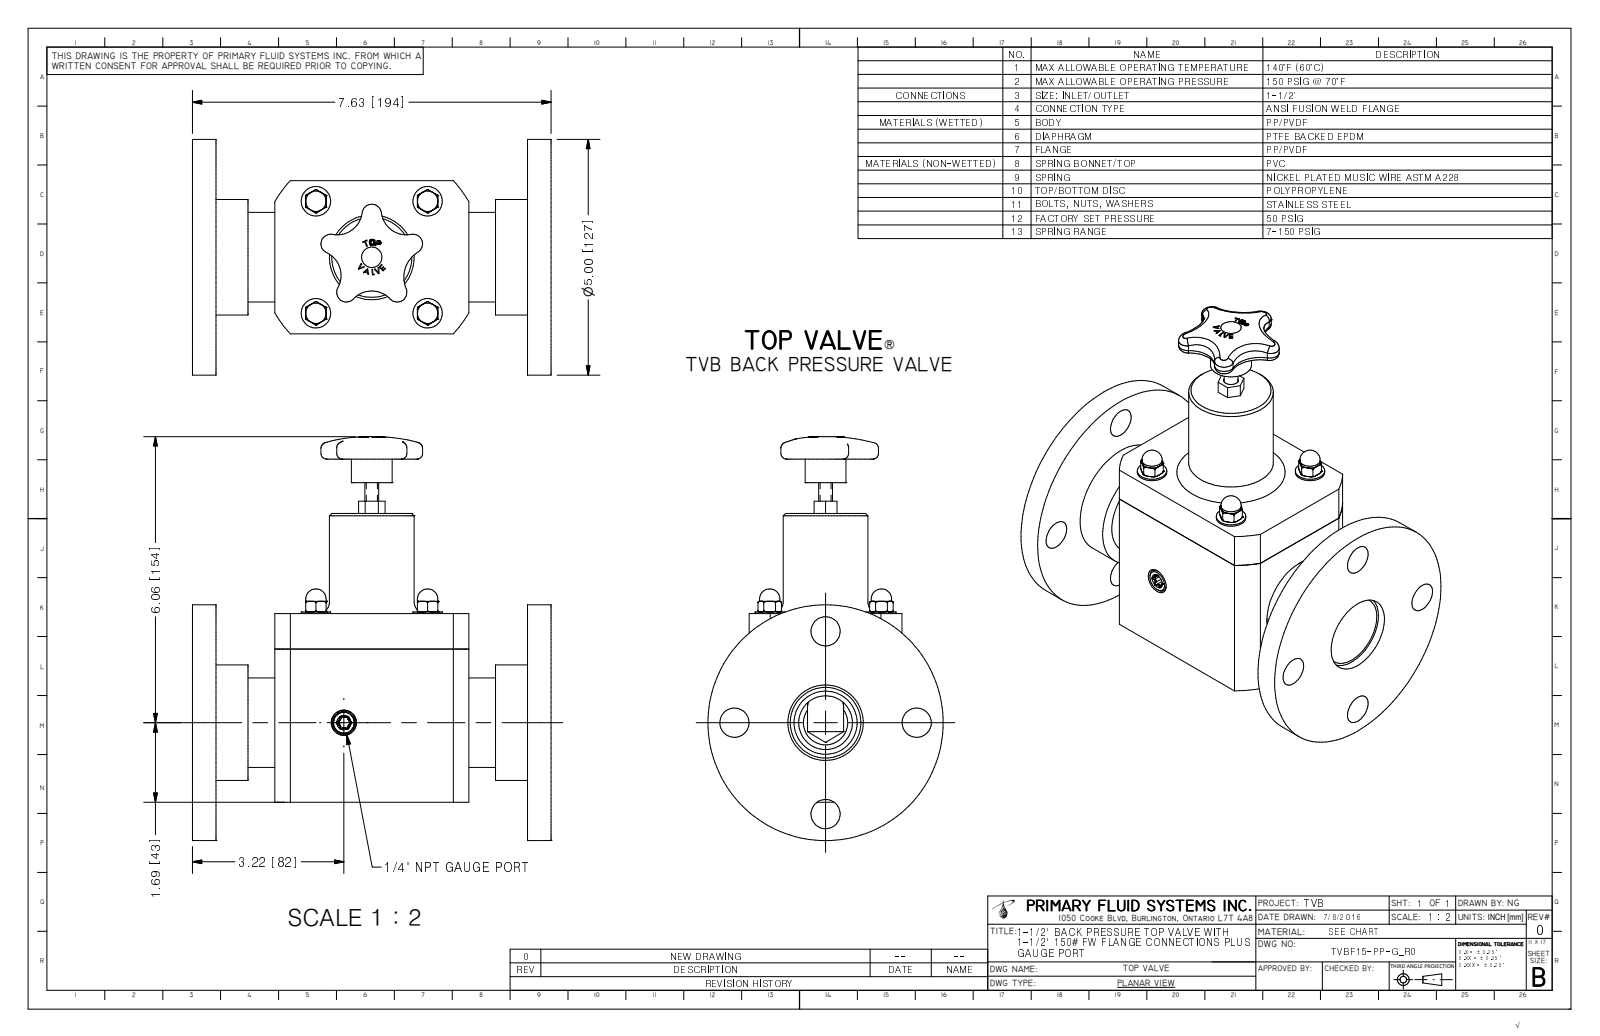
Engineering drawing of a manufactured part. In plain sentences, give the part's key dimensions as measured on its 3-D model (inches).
The part is named "TVBF15-PP-G_R0". Its 3-D file was written by "Autodesk Inventor 2009 (AUTOMOTIVE_DESIGN)". It is 1 solid with 383 faces: 160 planar, 67 cylindrical and 156 other. Overall it measures 8.565 by 7.625 by 5 inches. Its volume is 77.72 cubic inches and its surface area 239.2 square inches. Round holes: 4 of diameter 0.175, 4 of diameter 0.62, 1 of diameter 1.5, 1 of diameter 1.6. Round bosses or shafts: 4 of diameter 0.625, 4 of diameter 0.433, 4 of diameter 0.375, 1 of diameter 5, 1 of diameter 2.45, 1 of diameter 1.9, 1 of diameter 1.8, 1 of diameter 0.87. Partial cylindrical surfaces (rounded edges, fillets, slot ends): 6 of radius 0.027, 5 of radius 0.085, 5 of radius 0.205, 4 of radius 0.536, 4 of radius 0.656, 1 of radius 0.625, 1 of radius 0.745, 1 of radius 2.375. The main face-to-face distances are 0.5, 7.125, 7.625, 6.625, 3.25, 1.75, 5.875, 1.25, 5.375, 4. The hole center spacings are 1.937, 2.74, 2.375, 2.375, 3.359, 3.875.
